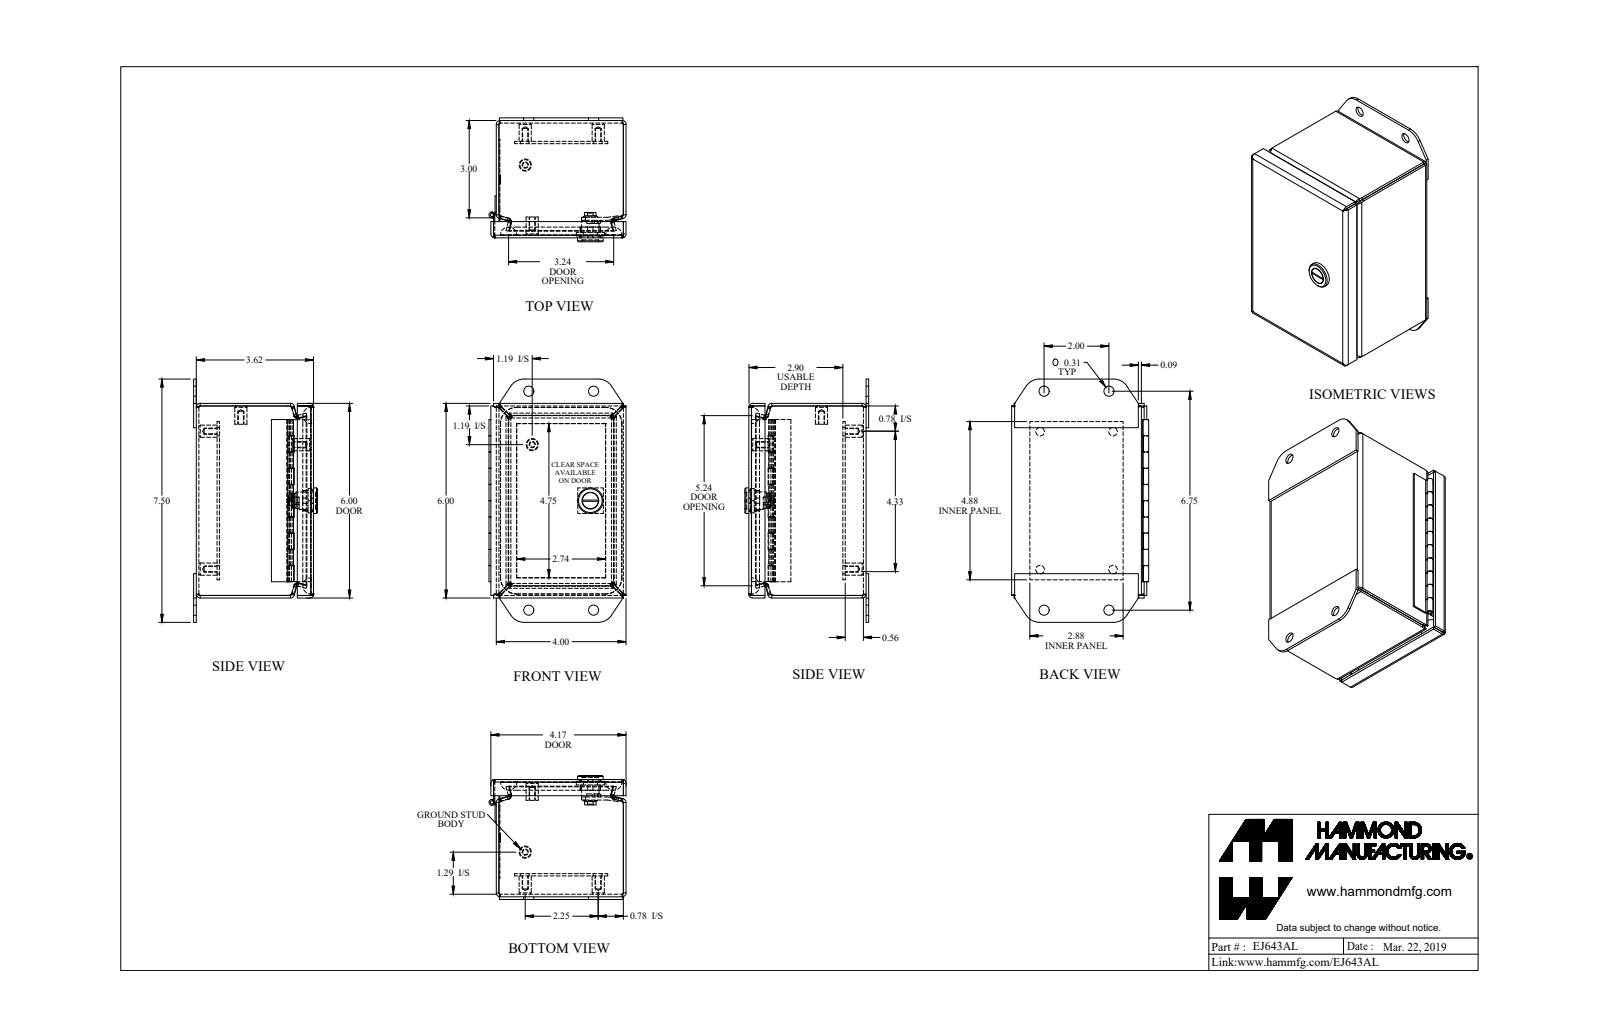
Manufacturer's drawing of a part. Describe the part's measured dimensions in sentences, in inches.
The part is named "EJ643AL_Default". Its 3-D file was written by "SolidWorks 2019 (CONFIG_CONTROL_DESIGN)". It is 14 solids with 550 faces: 330 planar, 152 cylindrical and 68 other. Overall it measures 7.5 by 4.226 by 3.82 inches. Its volume is 14.34 cubic inches and its surface area 367.7 square inches. Round holes: 6 of diameter 0.159, 4 of diameter 0.265, 4 of diameter 0.313, 1 of diameter 0.516. Round bosses or shafts: 6 of diameter 0.33, 5 of diameter 0.375, 1 of diameter 0.788, 1 of diameter 0.535, 1 of diameter 0.496, 1 of diameter 0.435, 1 of diameter 0.375, 1 of diameter 0.18. Partial cylindrical surfaces (rounded edges, fillets, slot ends): 16 of radius 0.041, 16 of radius 0.121, 12 of radius 0.281, 4 of radius 0.25, 4 of radius 0.499, 4 of radius 0.5, 2 of radius 0.06, 1 of radius 0.03. The main face-to-face distances are 0.081, 3.536, 3.919, 3.617, 5.919, 3.455, 4, 3.838, 0.643, 0.562. The hole center spacings are 0.024, 1.256, 2.25, 4.809, 5.501, 2, 2.137, 2.233.
